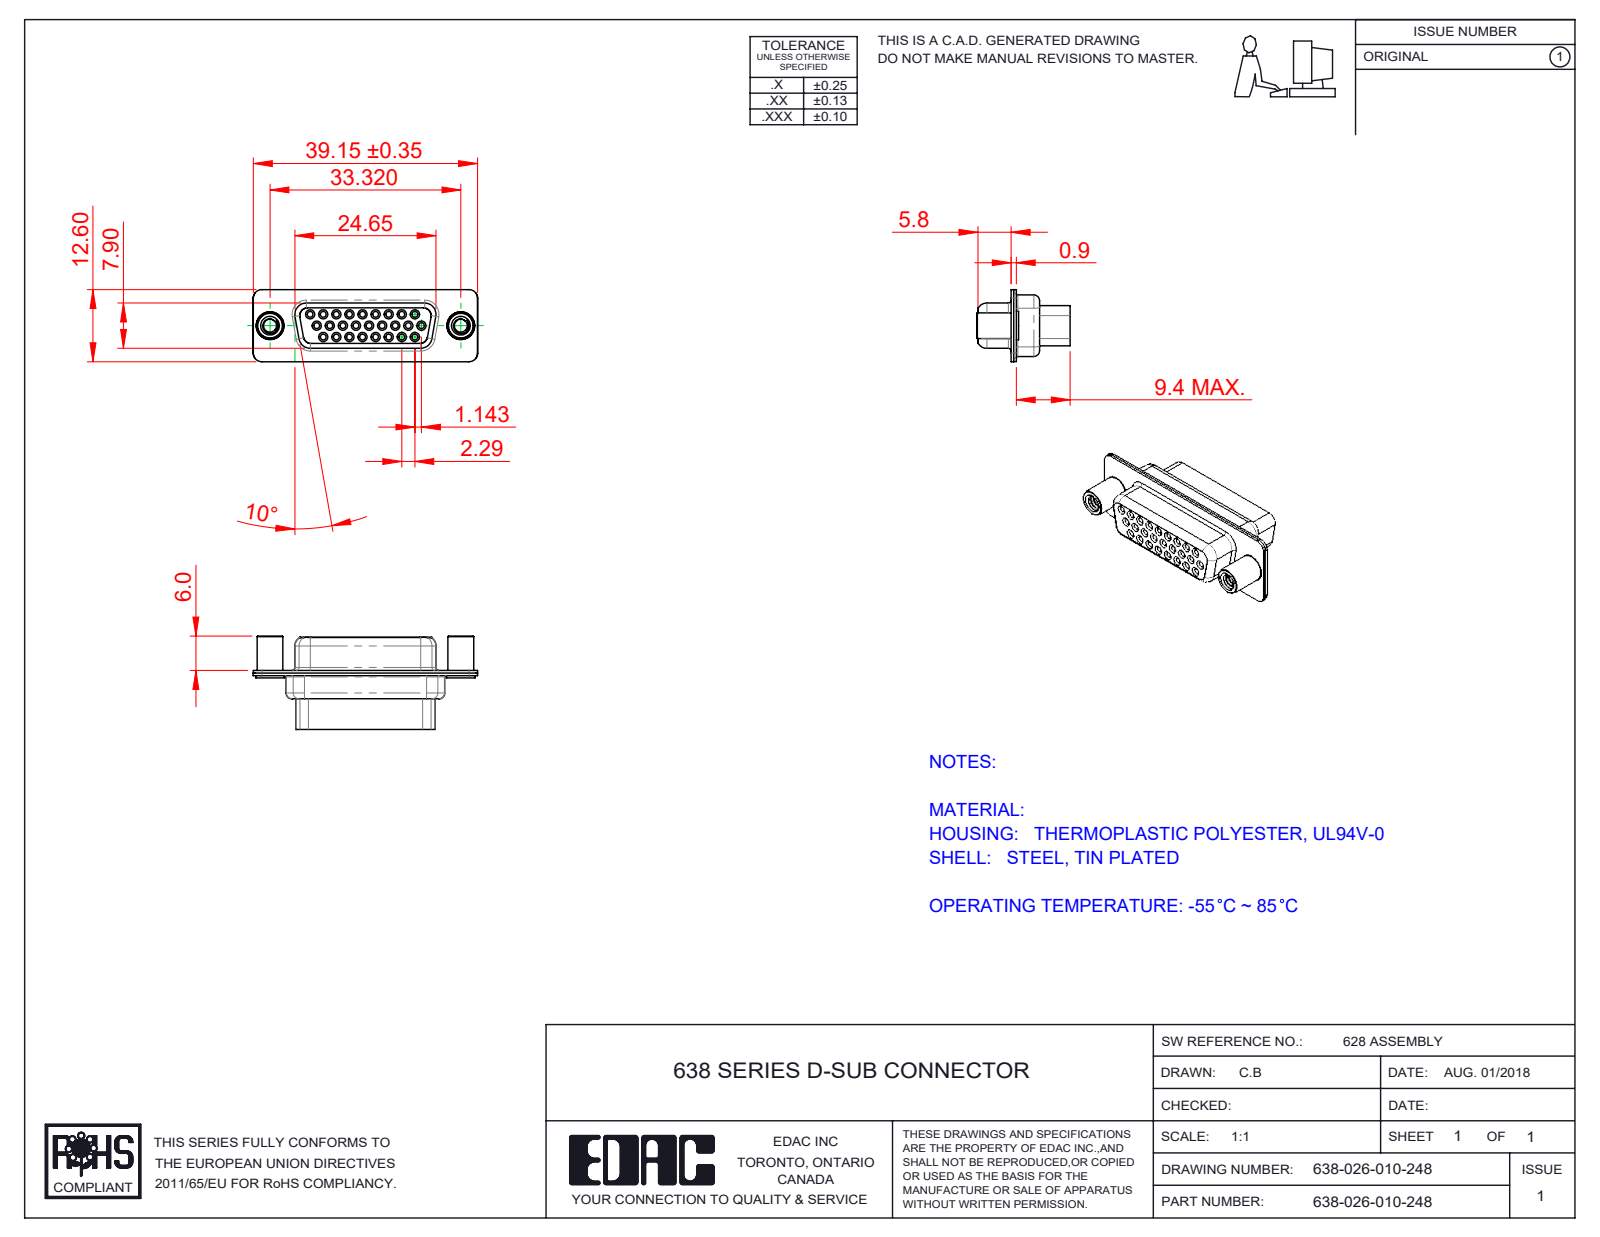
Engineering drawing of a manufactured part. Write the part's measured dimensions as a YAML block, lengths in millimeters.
part_name: "638 Shell Front_26 Contacts; 638 Shell Rear_26 Contacts; 638 Housing_26 Contacts HP; 638 4-40 Threaded Standoff (+1 more)"
step_written_by: "SolidWorks 2020 (CONFIG_CONTROL_DESIGN)"
units: millimeters
bodies: {solids: 5, faces: 651, planar: 147, cylindrical: 373, other: 131}
overall_size: [39.19, 16.3, 12.6]
volume: 2441
surface_area: 6632
round_holes:
  - {diameter: 1, count: 26}
  - {diameter: 1.7, count: 26}
  - {diameter: 1.8, count: 26}
  - {diameter: 2, count: 26}
  - {diameter: 2.26, count: 2}
  - {diameter: 4, count: 2}
  - {diameter: 4.05, count: 2}
  - {diameter: 4.85, count: 2}
round_bosses_or_shafts:
  - {diameter: 5, count: 2}
  - {diameter: 4.95, count: 2}
  - {diameter: 4.8, count: 2}
  - {diameter: 4.5, count: 2}
partial_cylinders:
  - {radius: 1.5, count: 20}
  - {radius: 2, count: 12}
  - {radius: 1.55, count: 8}
  - {radius: 1.35, count: 5}
  - {radius: 0.25, count: 4}
  - {radius: 0.5, count: 4}
  - {radius: 0.55, count: 4}
  - {radius: 0.7, count: 4}
face_to_face_distances: [0.45, 0.4, 6.6, 0.9, 1.43, 8.88, 7, 0.85, 6.2, 7.05]
hole_center_spacings: [3.96, 2.28, 4.57, 6.05, 2.29, 8.24, 6.86, 10.48]
